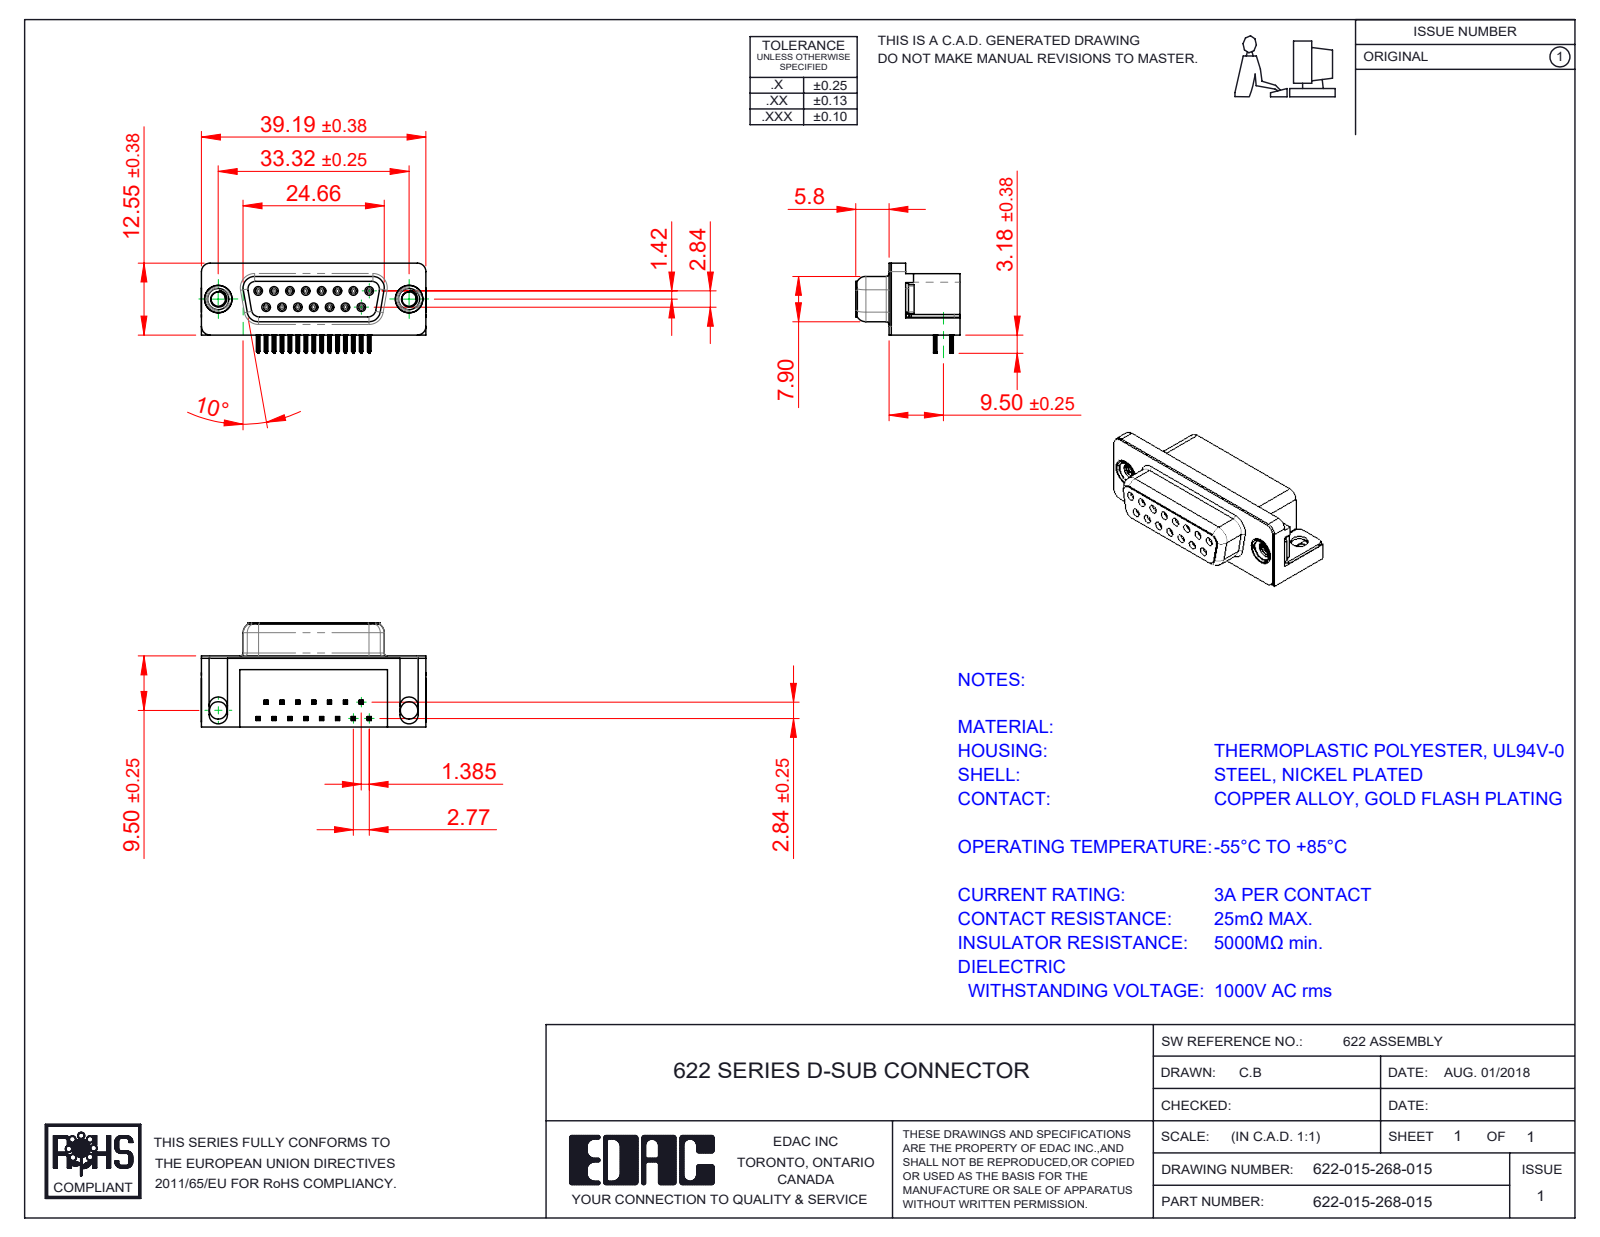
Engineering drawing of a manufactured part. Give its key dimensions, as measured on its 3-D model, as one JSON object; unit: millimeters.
{"part_name": "622-015-268-015; 622 Housing_15 Socket; 622 Contact Top; 622 M3 Threaded Rivet (+3 more)", "step_written_by": "SolidWorks 2016 (CONFIG_CONTROL_DESIGN)", "units": "millimeters", "bodies": {"solids": 21, "faces": 2425, "planar": 1072, "cylindrical": 609, "other": 744}, "overall_size": [39.22, 18.2, 15.73], "volume_mm3": 5181, "surface_area_mm2": 6706, "round_holes": [[0.8, 15], [0.9, 15], [2.5, 2], [3.05, 2], [4, 2], [4.8, 2], [5, 2]], "round_bosses_or_shafts": [[1.2, 15], [4.9, 2], [4.75, 2], [3.9, 2]], "partial_cylinders_radius": [[0.1, 120], [0.15, 60], [0.35, 30], [1, 18], [0.34, 15], [0.25, 8], [1.35, 8], [1.5, 8]], "face_to_face_distances": [0.4, 12, 6.2, 12.4, 10.35, 2.9, 6.65, 0.85, 0.35, 5.8], "hole_center_spacings": [3.16, 2.77, 5.54, 8.31, 11.08, 5.03, 5.04, 7.48]}
